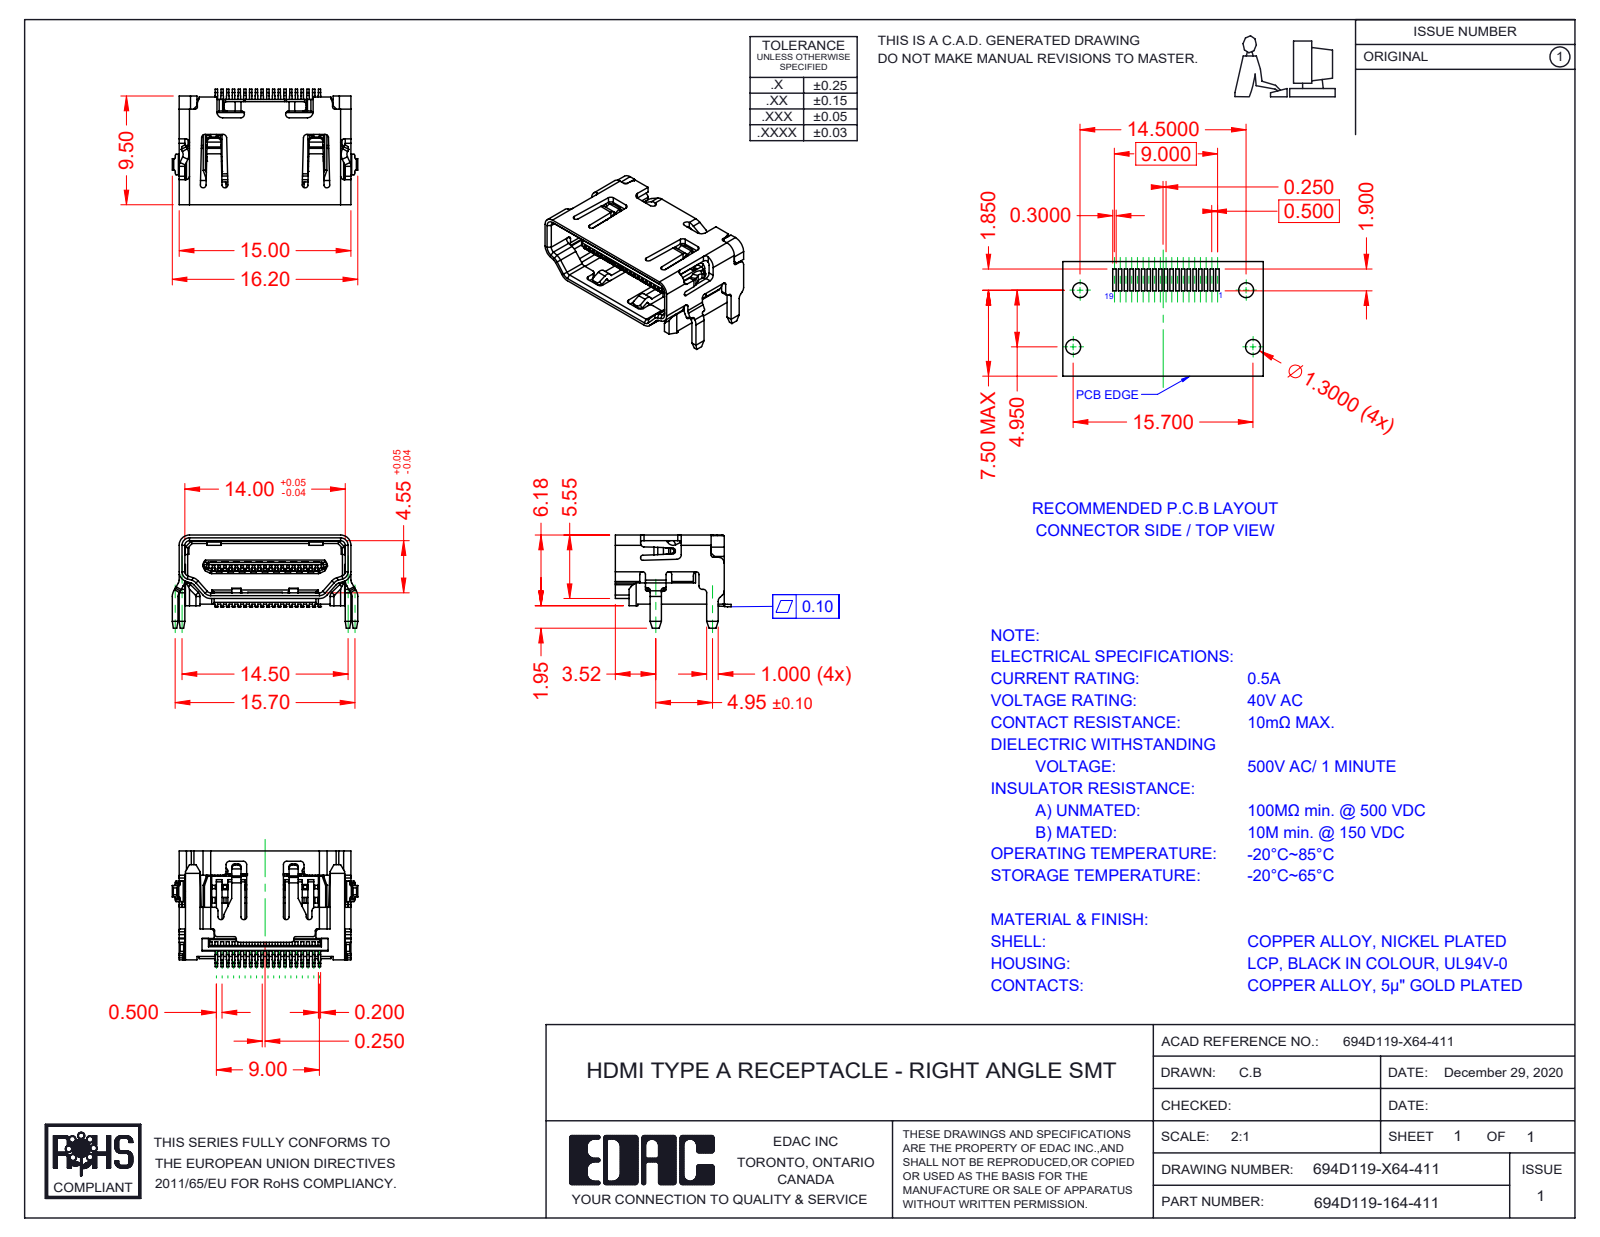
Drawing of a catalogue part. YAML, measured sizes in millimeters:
part_name: "694D119-164-411; Insulator 694D119-X64-411; Shell 694D119-X64-411"
step_written_by: "SolidWorks 2020 (AUTOMOTIVE_DESIGN)"
units: millimeters
bodies: {solids: 1, faces: 1591, planar: 1279, cylindrical: 240, other: 72}
overall_size: [16.2, 10.1, 8.13]
volume: 128
surface_area: 1207
partial_cylinders:
  - {radius: 0.2, count: 36}
  - {radius: 0.3, count: 31}
  - {radius: 0.25, count: 19}
  - {radius: 0.5, count: 19}
  - {radius: 1, count: 12}
  - {radius: 0.15, count: 10}
  - {radius: 0.4, count: 8}
  - {radius: 0.9, count: 6}
face_to_face_distances: [0.5, 5.05, 5.55, 2.4, 4.55, 14.5, 0.55, 14.45, 13.95, 0.84]
